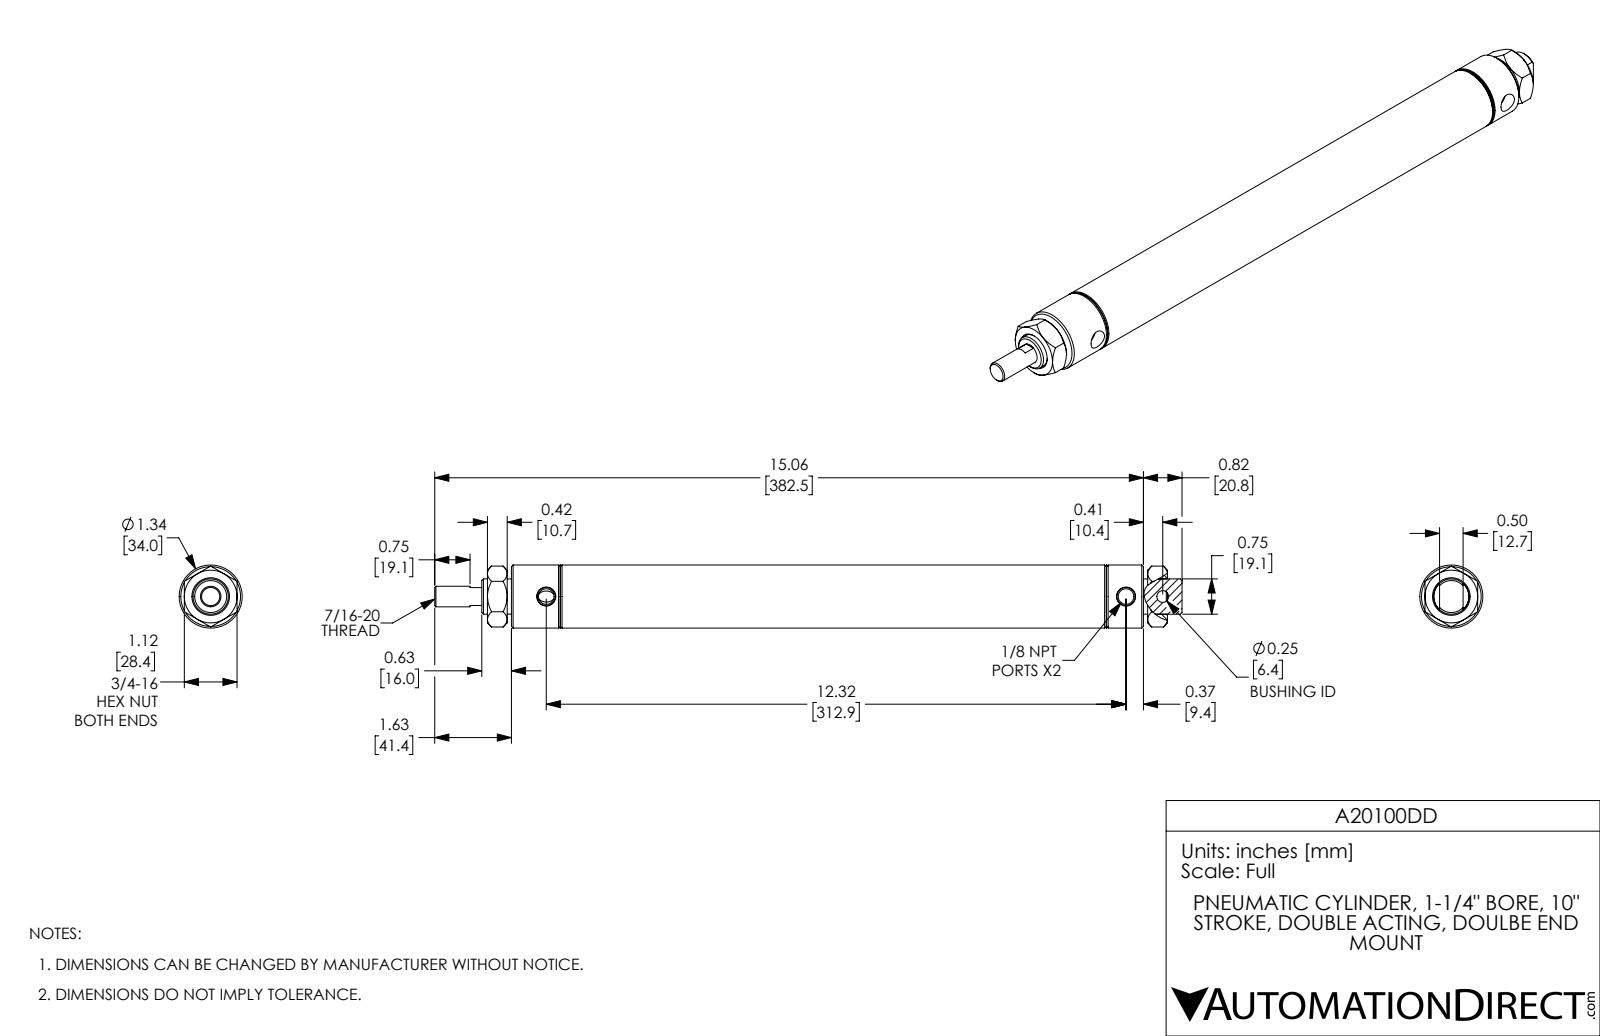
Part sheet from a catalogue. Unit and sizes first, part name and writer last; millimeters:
Units: millimetres
Overall size (bounding box): 403.4 × 34 × 34
Round holes (diameter × count): ⌀8.4 ×2, ⌀6.4 ×1, ⌀11.1 ×1, ⌀19.1 ×1, ⌀31.8 ×1
Round bosses / shafts (diameter × count): ⌀34 ×1, ⌀19 ×1
Main face-to-face distances: 37.2, 303.9, 12.7, 28.4, 266.7, 254, 7.9, 10.7, 356.4, 49.9
Hole centre spacings: 19.8, 312.9, 332.7
Volume: 151 900 mm³ · Surface area: 90 580 mm²
Bodies: 4 solids, 138 faces (44 planar, 36 cylindrical, 58 other)
Part name (STEP PRODUCT): A20100DD; A20100DD_Mounting Nut_D-3556; A20100DD-Rod; A20100DD-MainBody
STEP written by: SolidWorks 2017 (AUTOMOTIVE_DESIGN)
